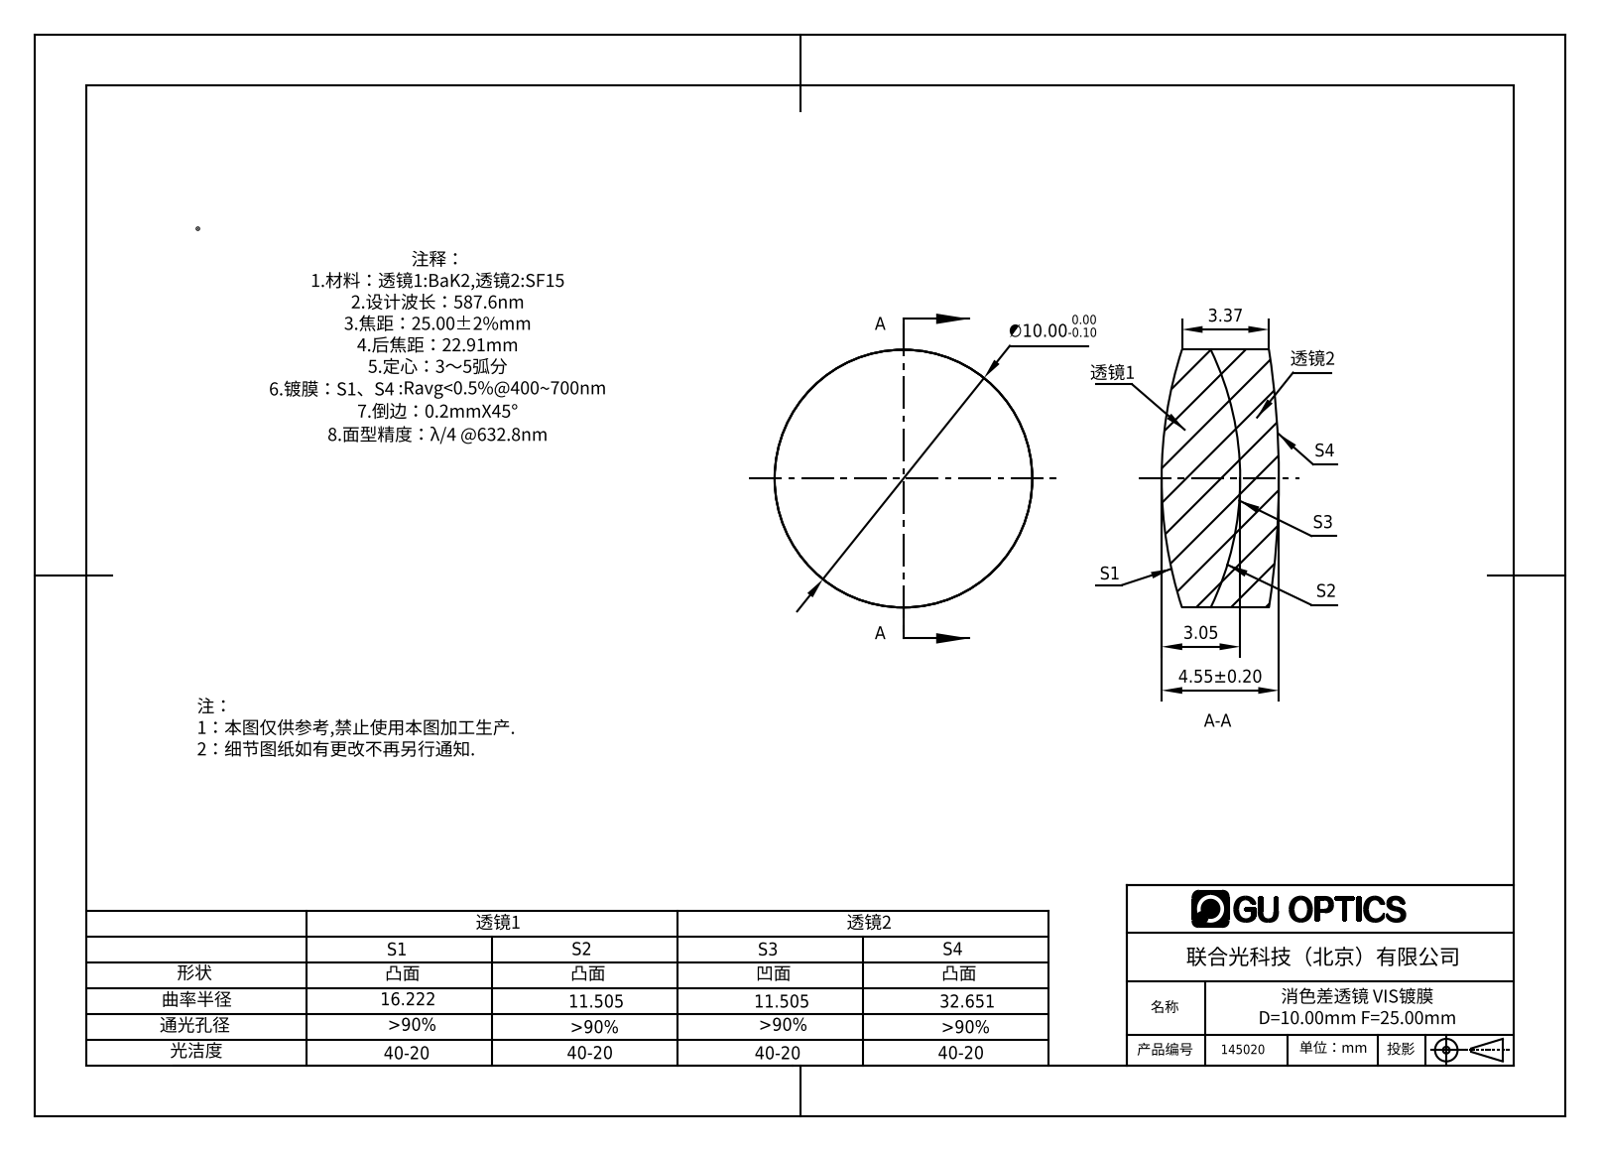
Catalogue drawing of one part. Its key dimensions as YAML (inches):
part_name: "145020"
step_written_by: "SolidWorks 2016 (AUTOMOTIVE_DESIGN)"
units: inches
bodies: {solids: 2, faces: 12, planar: 0, cylindrical: 4, other: 8}
overall_size: [0.394, 0.394, 0.179]
volume: 0.019
surface_area: 0.668
round_bosses_or_shafts:
  - {diameter: 0.394, count: 1}
